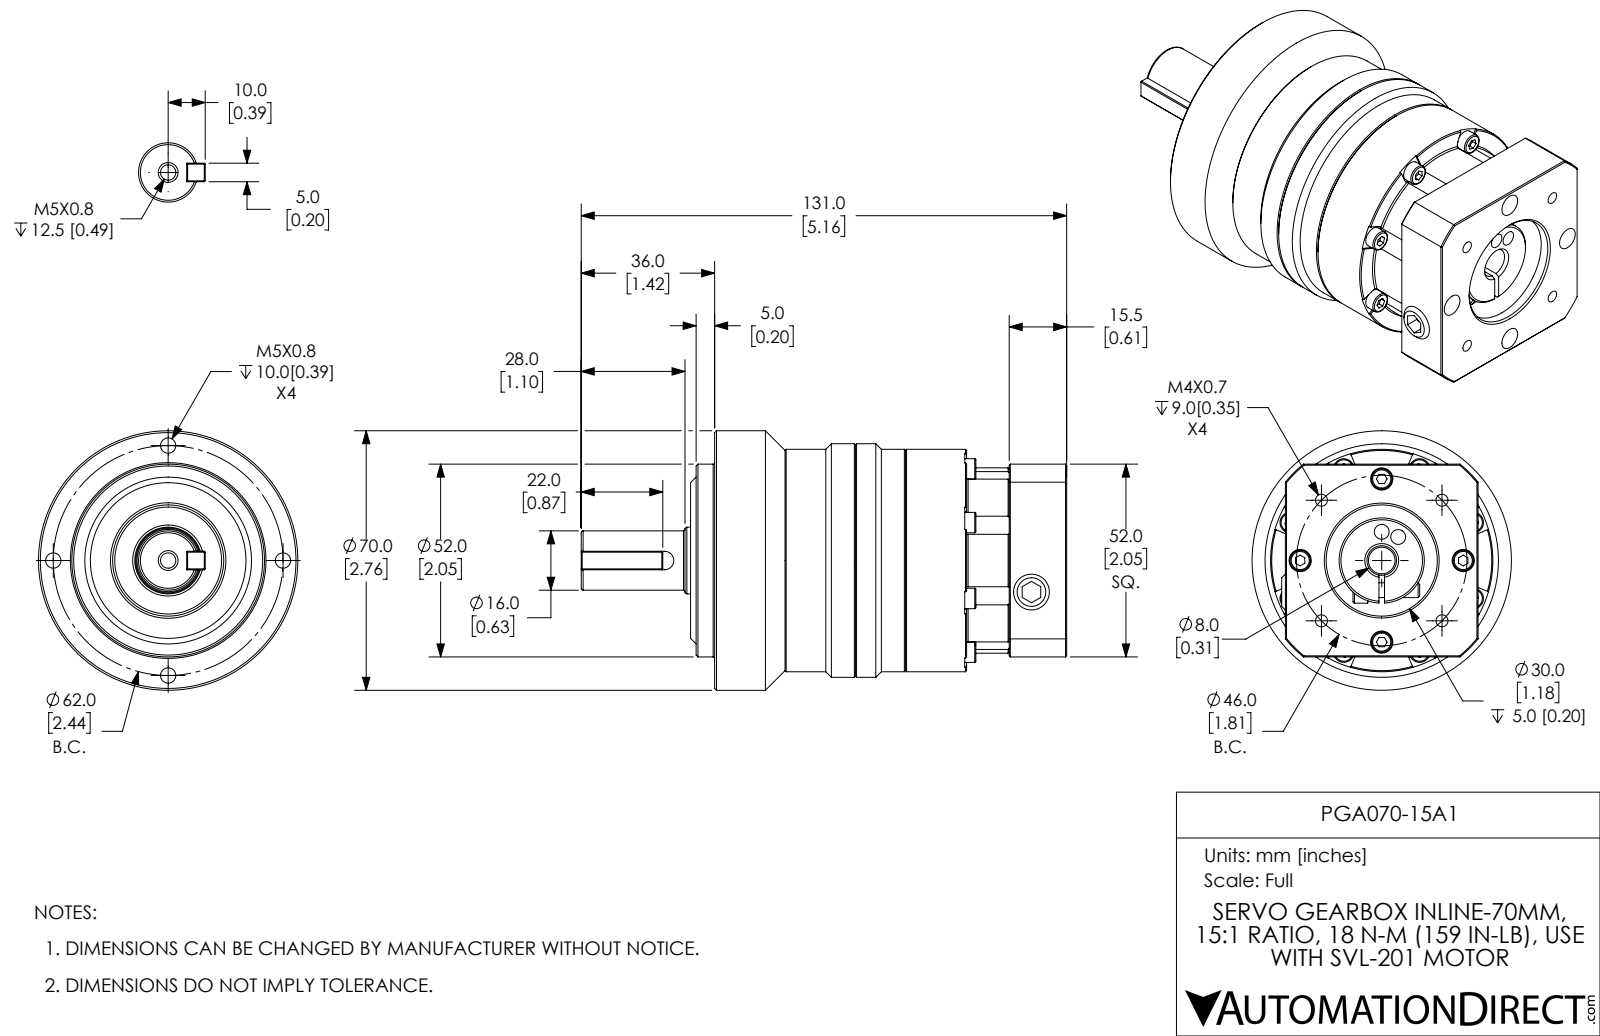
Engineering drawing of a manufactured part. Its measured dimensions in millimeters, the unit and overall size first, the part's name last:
Units: millimetres
Overall size (bounding box): 131 × 70 × 70
Round holes (diameter × count): ⌀4.13 ×5, ⌀3.24 ×4, ⌀6 ×4, ⌀4 ×2, ⌀8 ×2, ⌀4.5 ×1, ⌀30 ×1, ⌀34 ×1
Round bosses / shafts (diameter × count): ⌀5.5 ×12, ⌀70 ×1, ⌀63 ×1, ⌀60 ×1, ⌀52 ×1, ⌀23 ×1, ⌀18 ×1, ⌀16 ×1
Partial cylindrical surfaces — rounded edges, fillets, slot ends (radius × count): R3.25 ×8, R2.5 ×1, R4 ×1, R25 ×1, R26.75 ×1, R33.5 ×1
Main face-to-face distances: 95, 15.5, 79.5, 86, 52, 6.5, 101.5, 5, 1.5, 27
Hole centre spacings: 17.24, 21.95, 38.01, 41.57, 49.98, 9, 22, 23
Volume: 281 581 mm³ · Surface area: 37 208 mm²
Bodies: 1 solid, 495 faces (199 planar, 129 cylindrical, 167 other)
Part name (STEP PRODUCT): PGA070-15A1
STEP written by: SolidWorks 2019 (CONFIG_CONTROL_DESIGN)
